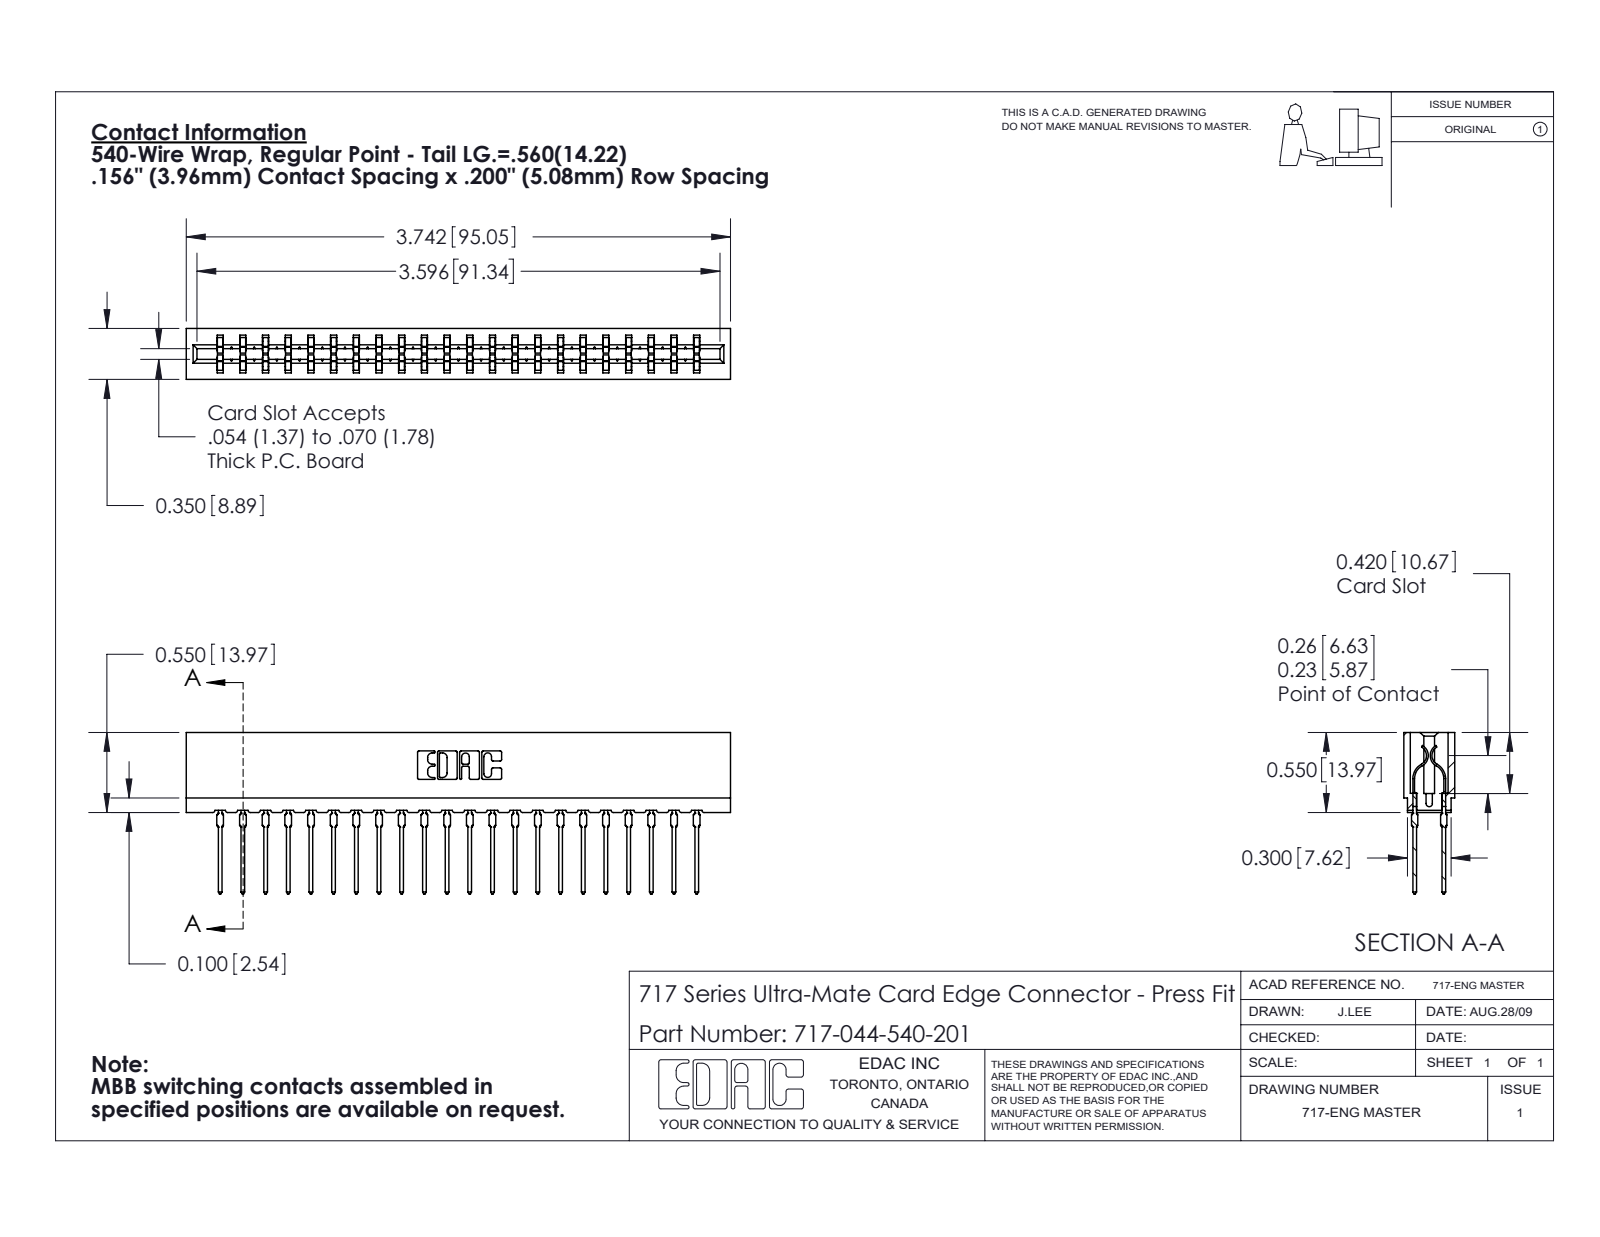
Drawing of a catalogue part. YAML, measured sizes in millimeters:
part_name: "745-292-001_540; 717 Part_Insulator Option - 06; 717-044-540-201"
step_written_by: "SolidWorks 2020 (CONFIG_CONTROL_DESIGN)"
units: millimeters
bodies: {solids: 45, faces: 4054, planar: 2100, cylindrical: 810, other: 1144}
overall_size: [95, 28.2, 8.9]
volume: 8460
surface_area: 13230
partial_cylinders:
  - {radius: 0.5, count: 88}
  - {radius: 0.4, count: 44}
  - {radius: 0.3, count: 22}
  - {radius: 0.1, count: 8}
  - {radius: 0.3, count: 8}
  - {radius: 0.2, count: 6}
  - {radius: 0.8, count: 6}
  - {radius: 0.7, count: 3}
face_to_face_distances: [5.4, 3.5, 8.9, 1.6, 7.3, 1.9, 3.8, 4, 1.9, 15.8]
